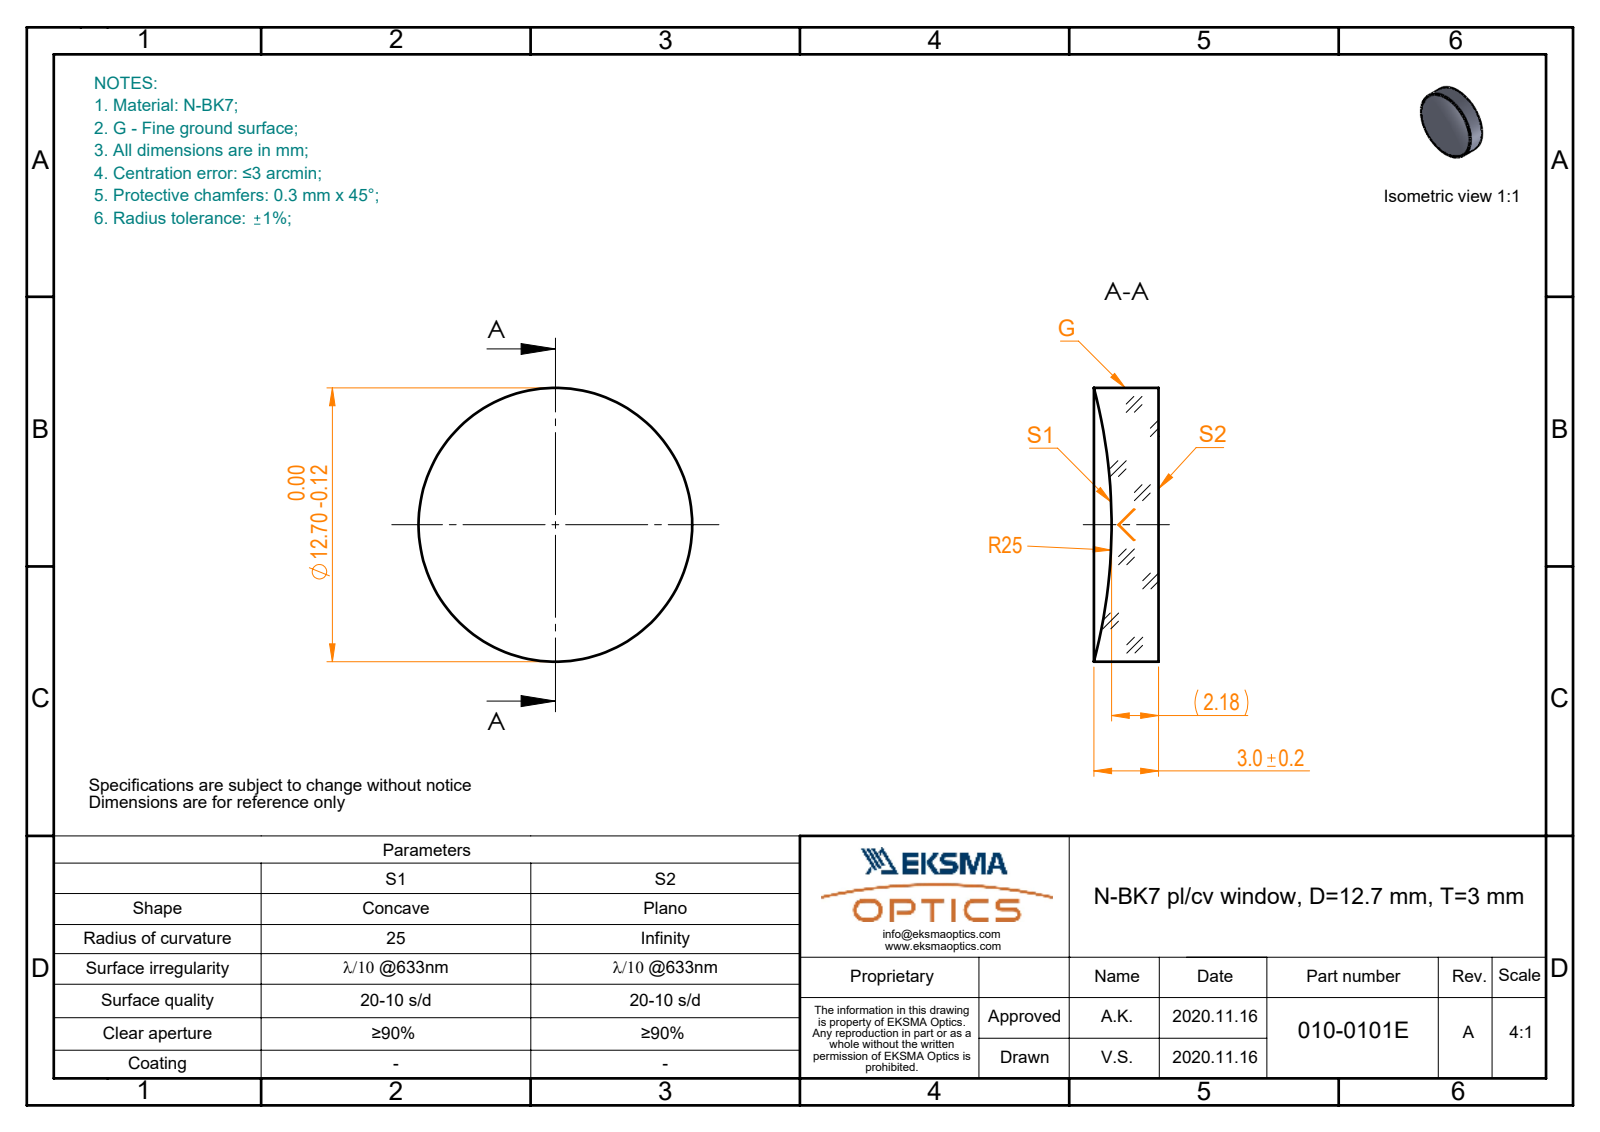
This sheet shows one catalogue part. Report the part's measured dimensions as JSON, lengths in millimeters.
{"part_name": "010-0101E_N-BK7_PCV_window", "step_written_by": "SolidWorks 2019 (CONFIG_CONTROL_DESIGN)", "units": "millimeters", "bodies": {"solids": 1, "faces": 5, "planar": 1, "cylindrical": 2, "other": 2}, "overall_size": [12.7, 12.7, 3], "volume_mm3": 328, "surface_area_mm2": 375, "round_bosses_or_shafts": [[12.7, 1]]}
